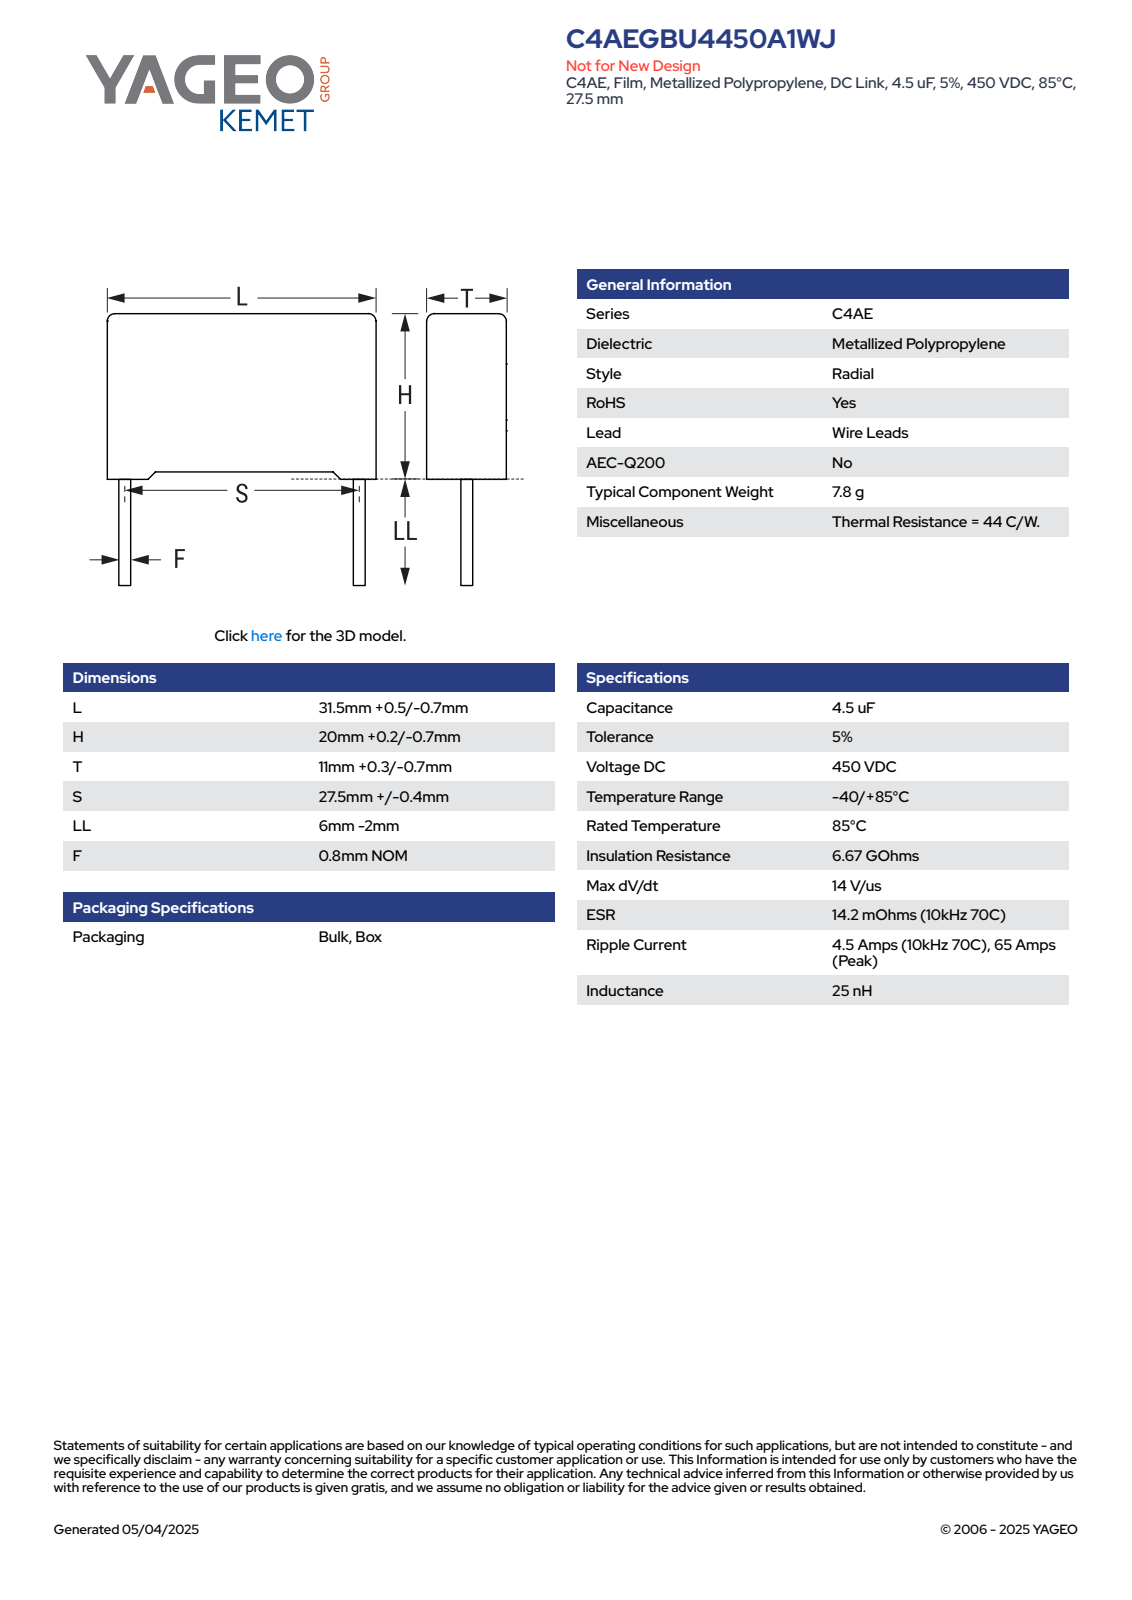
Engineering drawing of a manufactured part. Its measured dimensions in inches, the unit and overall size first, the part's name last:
Units: inches
Overall size (bounding box): 1.26 × 0.953 × 0.445
Round bosses / shafts (diameter × count): ⌀0.031 ×2
Partial cylindrical surfaces — rounded edges, fillets, slot ends (radius × count): R0.02 ×4
Main face-to-face distances: 0.445, 0.766, 1.26, 0.768, 0.028, 0.03, 0.795, 0.042, 0.445, 1.218
Volume: 0.431 in³ · Surface area: 3.949 in²
Bodies: 4 solids, 85 faces (77 planar, 8 cylindrical, 0 other)
Part name (STEP PRODUCT): CFR_RB2CFP_31.5X20X11_L32H20.2T11.3S27.5LL4F0.8
STEP written by: SolidWorks 2014 (AUTOMOTIVE_DESIGN)
